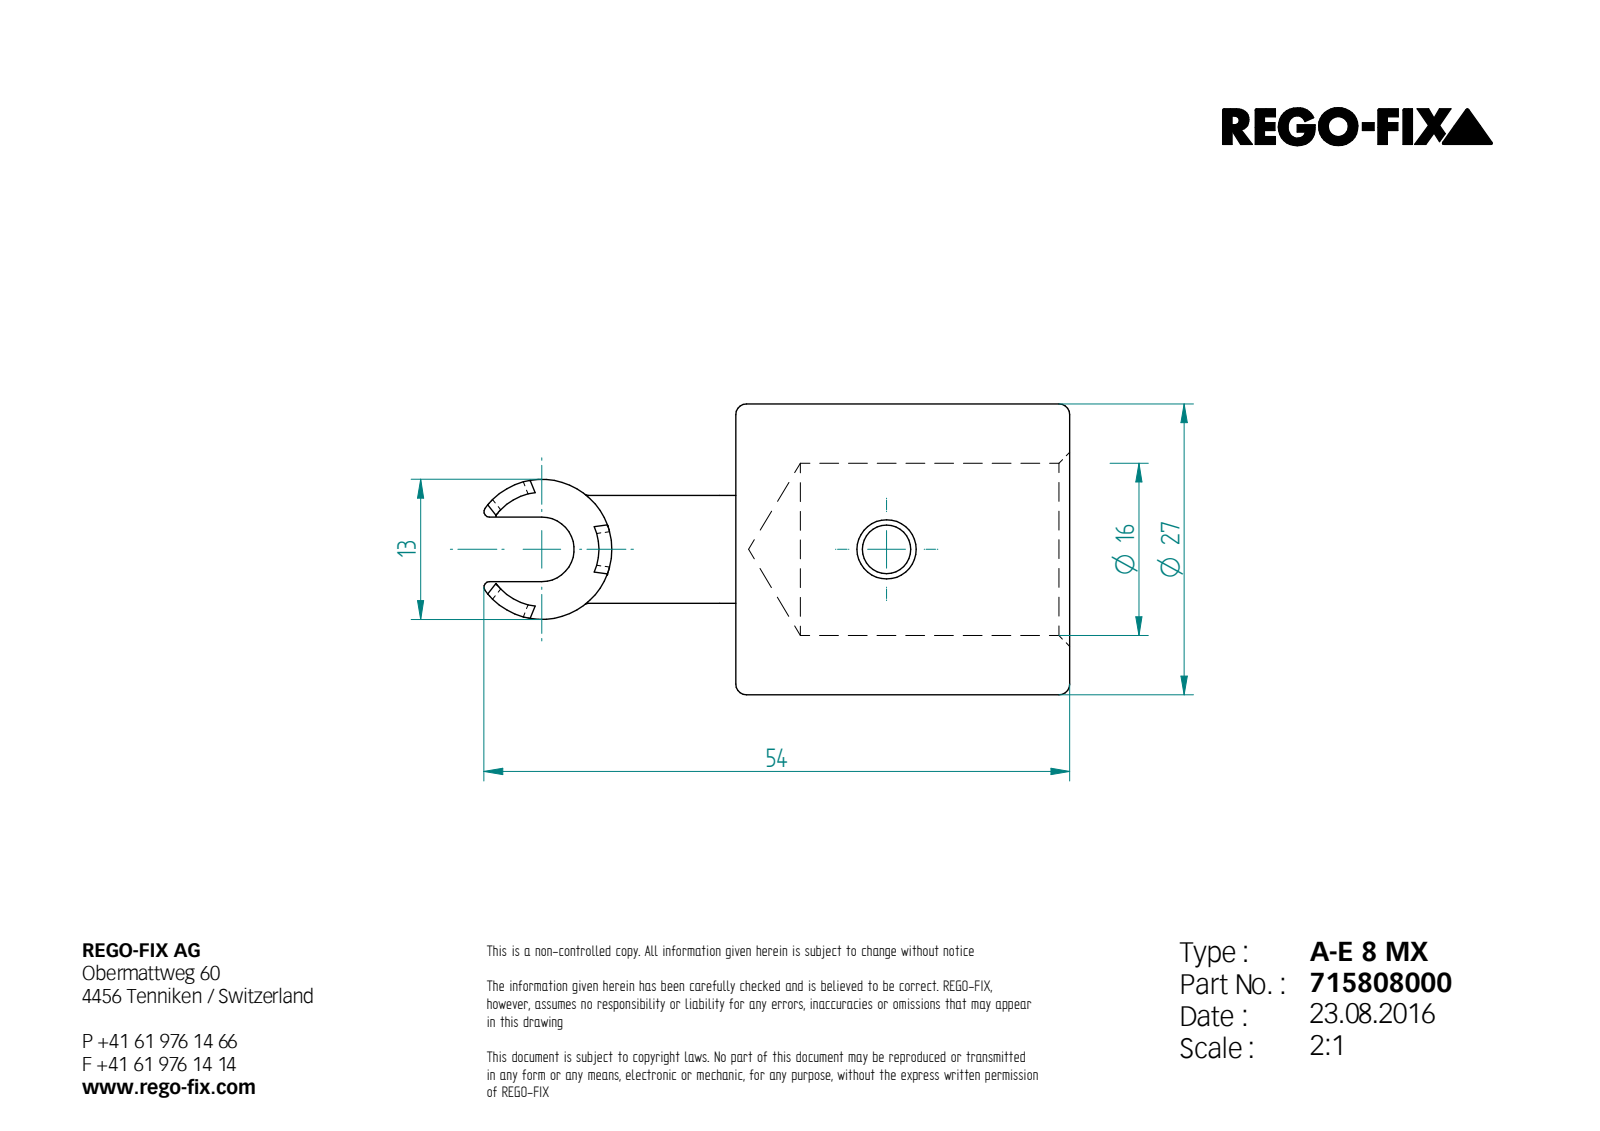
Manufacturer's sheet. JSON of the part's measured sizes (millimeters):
{"step_written_by": "Unknown (AUTOMOTIVE_DESIGN)", "units": "millimeters", "bodies": {"solids": 1, "faces": 64, "planar": 20, "cylindrical": 25, "other": 19}, "overall_size": [54.37, 27, 27], "volume_mm3": 12773, "surface_area_mm2": 5823, "round_holes": [[4.5, 1], [5.5, 1], [16, 1]], "round_bosses_or_shafts": [[27, 1], [13, 1]], "partial_cylinders_radius": [[0.65, 6], [0.5, 4], [1.5, 4], [3, 1], [4, 1], [5.3, 1]], "face_to_face_distances": [31, 5.4, 2.4, 3, 6, 8, 2.6, 5, 1, 7]}
